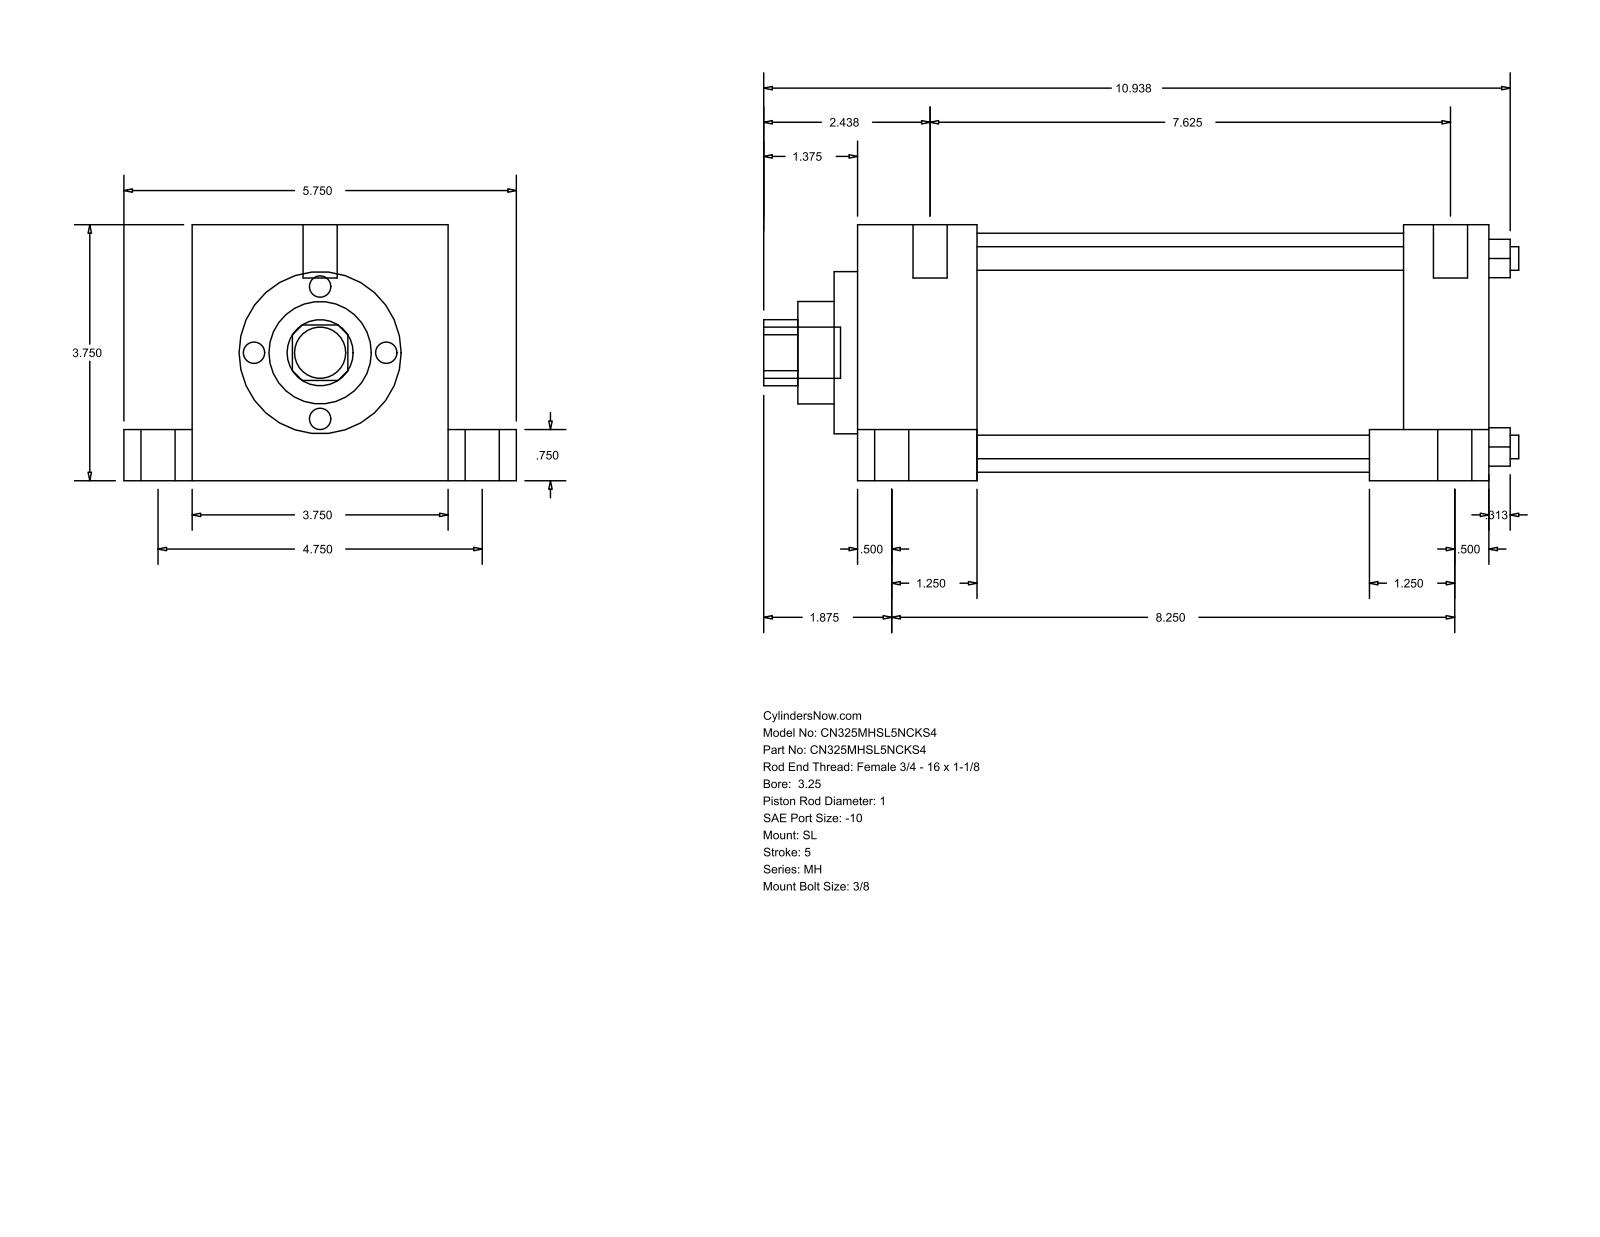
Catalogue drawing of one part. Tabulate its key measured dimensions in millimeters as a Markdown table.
| quantity | value |
| --- | --- |
| part name | MH_SL__0325_1 |
| STEP written by | GSSL Pune (CONFIG_CONTROL_DESIGN) |
| units | millimeters |
| bodies | 0 solids, 110 faces (77 planar, 33 cylindrical, 0 other) |
| overall size | 280.99 × 146.05 × 95.25 |
| round holes (diameter × count) | 8.76 × 4, 25.4 × 1, 38.1 × 1, 60.33 × 1, 88.9 × 1 |
| round bosses / shafts (diameter × count) | 12.7 × 6, 19.05 × 5, 5.56 × 4 |
| partial cylindrical surfaces (radius × count) | 12.29 × 1 |
| main face-to-face distances | 95.24, 234.96, 44.46, 190.5, 25.41, 120.65, 19.05, 76.19, 203.2, 158.74 |
| hole center spacings | 49.57, 70.1, 99.14 |
